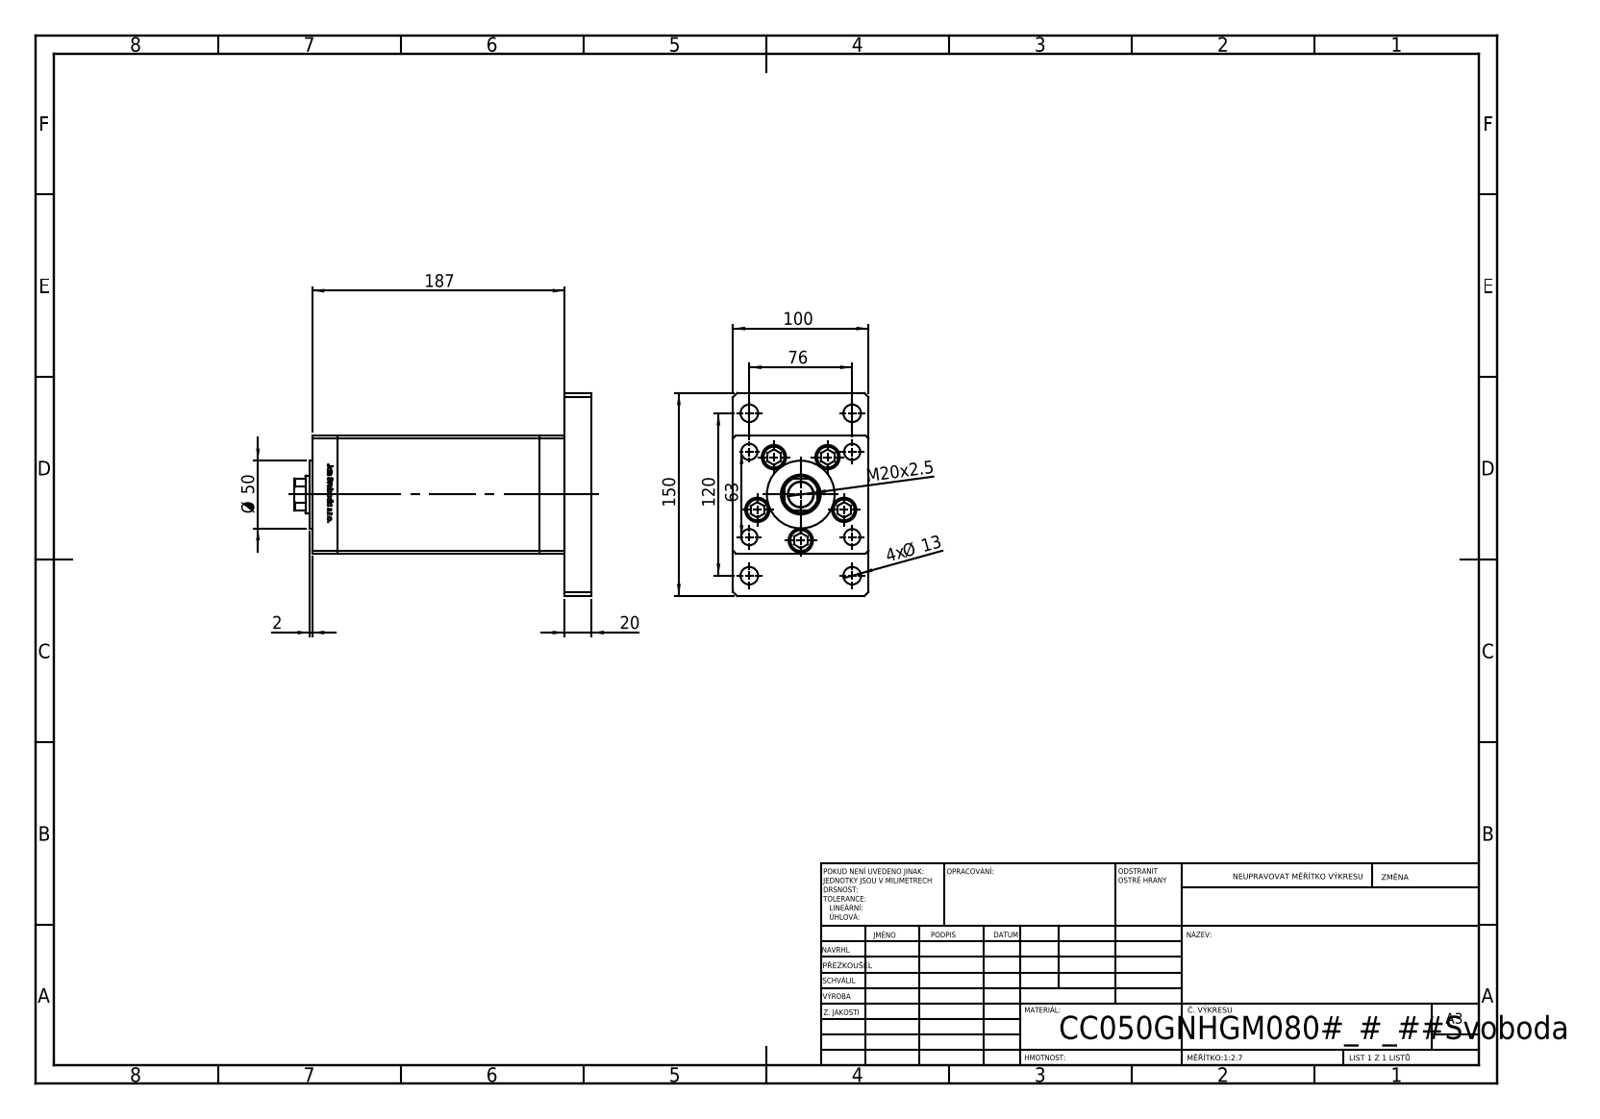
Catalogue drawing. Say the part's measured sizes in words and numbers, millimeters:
The part is named "V220C_VC_G; V220C BACK_G; V220C_F; V220C_FRONT_G (+2 more)". Its 3-D file was written by "SolidWorks 2019 (CONFIG_CONTROL_DESIGN)". It is 19 solids with 1308 faces: 515 planar, 187 cylindrical and 606 other. Overall it measures 219.5 by 150 by 100 millimeters. Its volume is 1 697 000 cubic millimeters and its surface area 256 607 square millimeters. Round holes: 9 of diameter 12, 5 of diameter 13.5, 5 of diameter 18, 4 of diameter 13, 4 of diameter 17, 2 of diameter 2, 2 of diameter 13.16, 1 of diameter 18.5, 1 of diameter 28, 1 of diameter 29.5, 1 of diameter 68. Round bosses or shafts: 9 of diameter 8, 5 of diameter 17, 1 of diameter 50. Partial cylindrical surfaces (rounded edges, fillets, slot ends): 2 of radius 0.93, 1 of radius 13.5. The main face-to-face distances are 19, 100, 167.5, 87, 148.5, 20, 187.5, 39, 206.5, 186.5. The hole center spacings are 34, 28.5, 49.36, 71.02, 76, 81.17, 91.5, 118.95.
